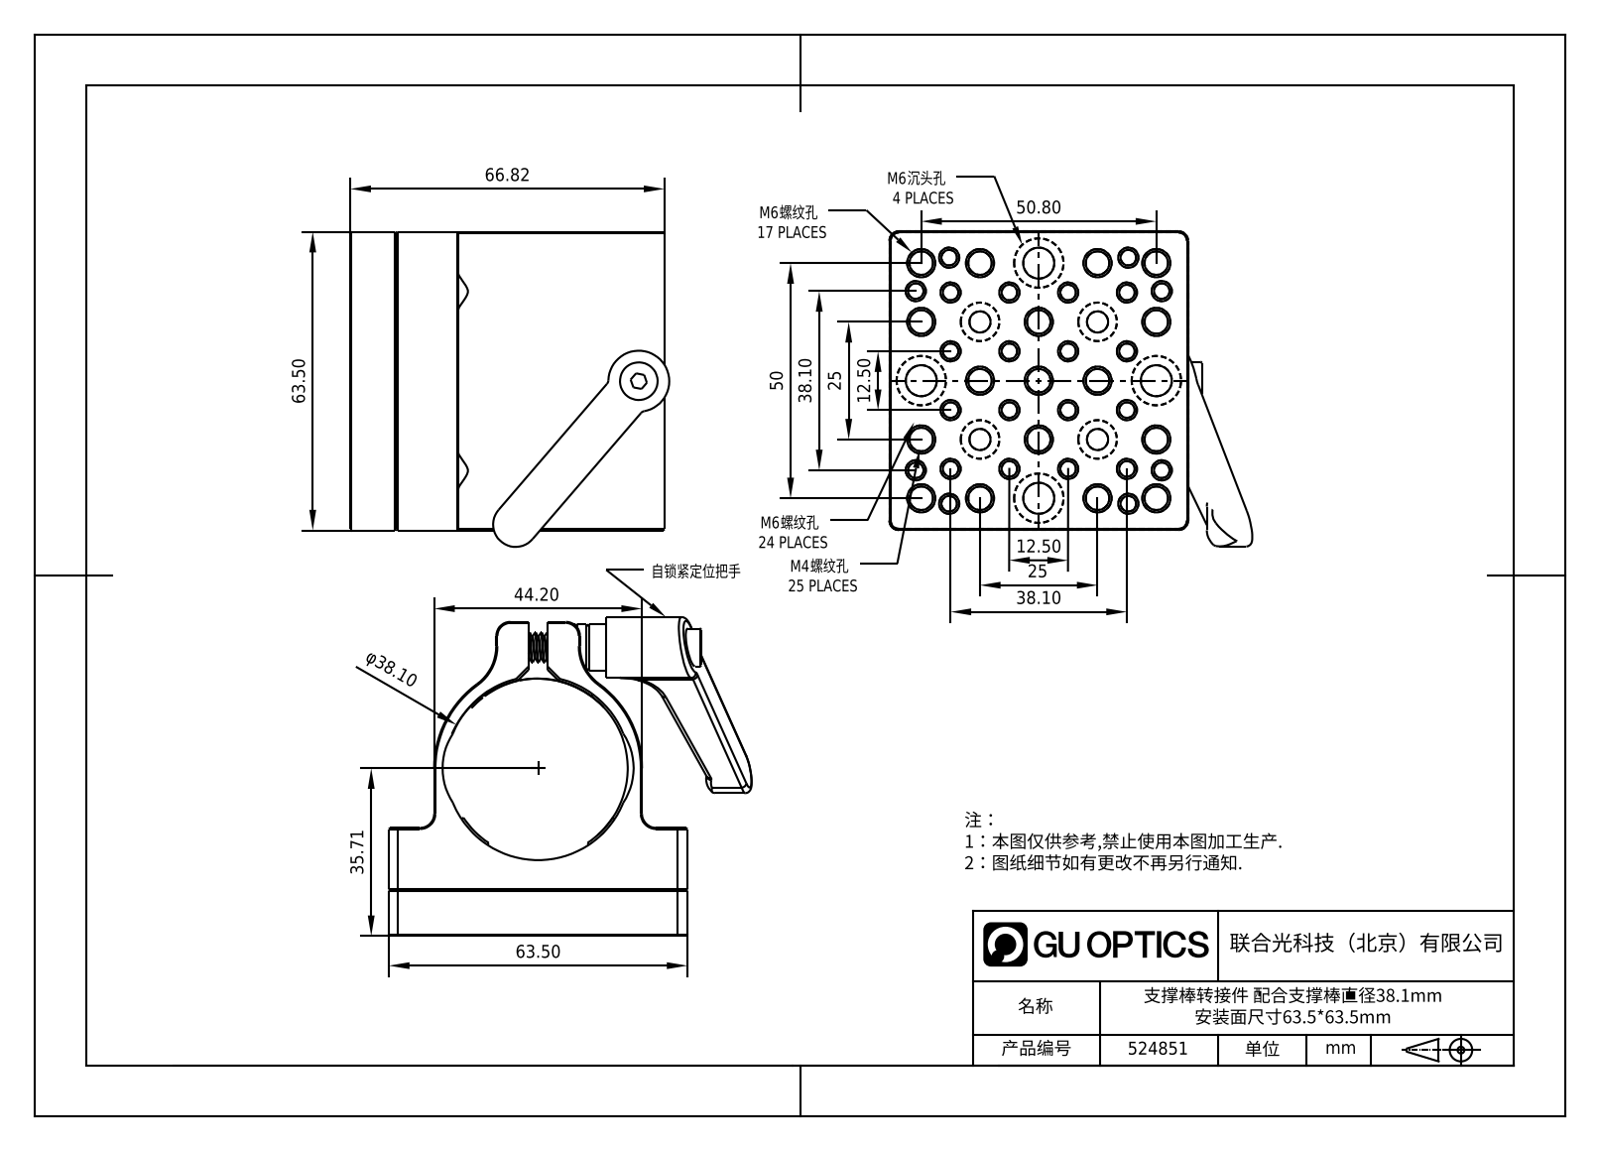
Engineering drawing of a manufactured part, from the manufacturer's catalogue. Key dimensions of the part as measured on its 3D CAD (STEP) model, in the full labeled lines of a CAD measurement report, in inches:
Part name (STEP PRODUCT): 1.4.3.33-ZGZ-1.5-JK
STEP written by: SolidWorks 2021 (CONFIG_CONTROL_DESIGN)
Units: inches
Bodies: 0 solids, 441 faces (98 planar, 181 cylindrical, 162 other)
Overall size (bounding box): 3.039 × 2.671 × 2.637
Round holes (diameter × count): ⌀0.13 ×24, ⌀0.197 ×18, ⌀0.26 ×5, ⌀0.413 ×5, ⌀0.177 ×4, ⌀0.307 ×4
Round bosses / shafts (diameter × count): ⌀0.51 ×1, ⌀0.39 ×1, ⌀0.315 ×1, ⌀0.25 ×1
Partial cylindrical surfaces — rounded edges, fillets, slot ends (radius × count): R0.04 ×4, R0.079 ×4, R0.118 ×4, R0.05 ×2, R0.394 ×2, R0.525 ×2, R0.015 ×1, R0.187 ×1
Main face-to-face distances: 2.5, 0.791, 1.171, 1.329, 0.38, 2.12, 0.949, 0.906, 0.157, 1.74
Hole centre spacings: 1.1, 0.492, 0.696, 1.556, 0.984, 1.774, 1.476, 1.392
